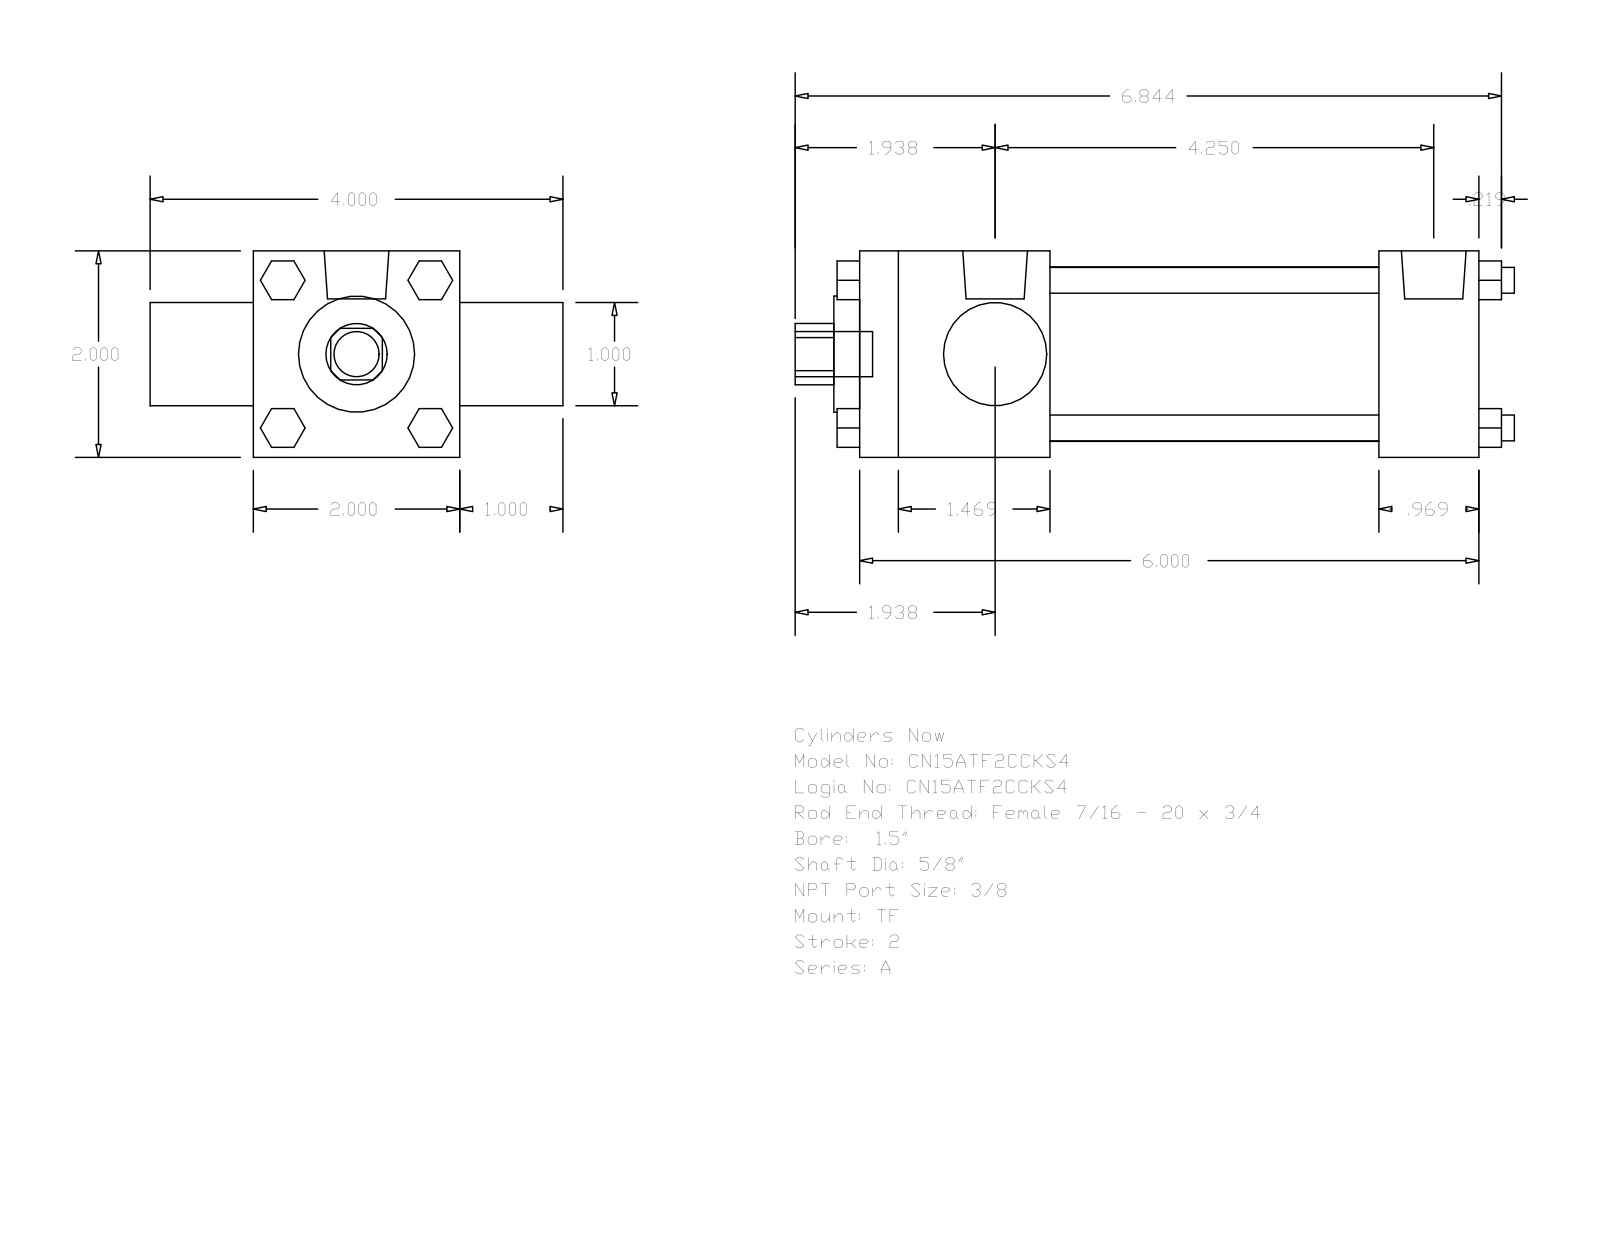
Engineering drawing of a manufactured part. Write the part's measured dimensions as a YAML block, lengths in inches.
part_name: "A_TF__0150_0.625"
step_written_by: "GSSL Pune (CONFIG_CONTROL_DESIGN)"
units: inches
bodies: {solids: 0, faces: 120, planar: 92, cylindrical: 28, other: 0}
overall_size: [6.969, 4, 2]
round_holes:
  - {diameter: 0.625, count: 1}
  - {diameter: 1, count: 1}
  - {diameter: 1.125, count: 1}
  - {diameter: 1.69, count: 1}
round_bosses_or_shafts:
  - {diameter: 0.25, count: 4}
  - {diameter: 0.219, count: 3}
  - {diameter: 0.627, count: 2}
  - {diameter: 0.437, count: 1}
partial_cylinders:
  - {radius: 0.297, count: 1}
face_to_face_distances: [2, 6, 1, 3, 1.844, 5.031, 3.187, 4.156, 0.969, 0.375]
